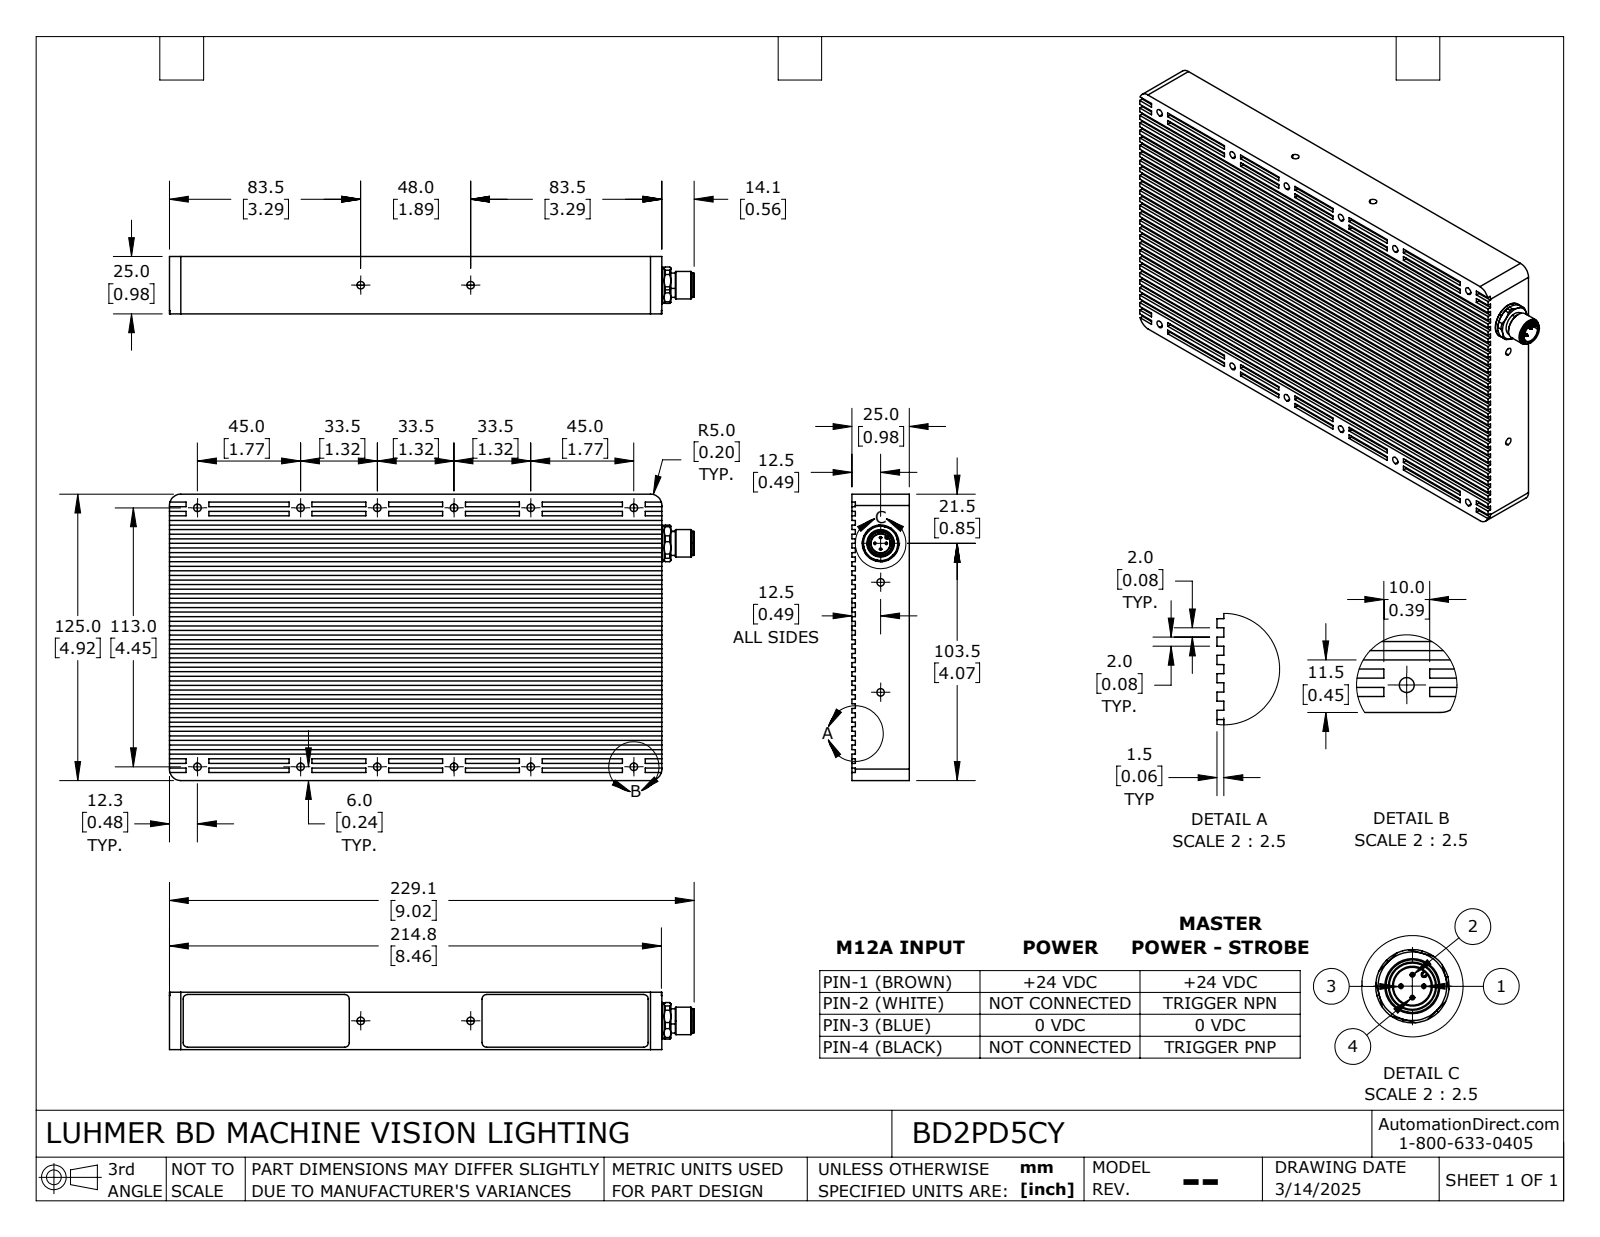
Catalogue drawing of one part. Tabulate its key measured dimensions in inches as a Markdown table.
| quantity | value |
| --- | --- |
| part name | BD2__5_Y |
| STEP written by | SolidWorks 2024 (AUTOMOTIVE_DESIGN) |
| units | inches |
| bodies | 1 solid, 1620 faces (330 planar, 816 cylindrical, 474 other) |
| overall size | 9.02 × 4.921 × 0.984 |
| volume | 38.92 in³ |
| surface area | 145.9 in² |
| round holes (diameter × count) | 0.134 × 18, 0.13 × 16, 0.057 × 4, 0.327 × 1, 0.37 × 1 |
| round bosses / shafts (diameter × count) | 0.22 × 18, 0.114 × 18, 0.031 × 18, 0.055 × 4, 0.039 × 4, 0.63 × 1, 0.473 × 1, 0.417 × 1 |
| partial cylindrical surfaces (radius × count) | 0.022 × 216, 0.01 × 108, 0.04 × 18, 0.079 × 8, 0.138 × 4, 0.197 × 4, 0.012 × 2, 0.024 × 1 |
| main face-to-face distances | 0.965, 0.059, 0.906, 0.079, 0.157, 0.236, 0.315, 0.394, 0.472, 4.906 |
| hole center spacings | 4.507, 4.659, 1.319, 1.32, 1.321, 4.449, 4.507, 4.64 |
